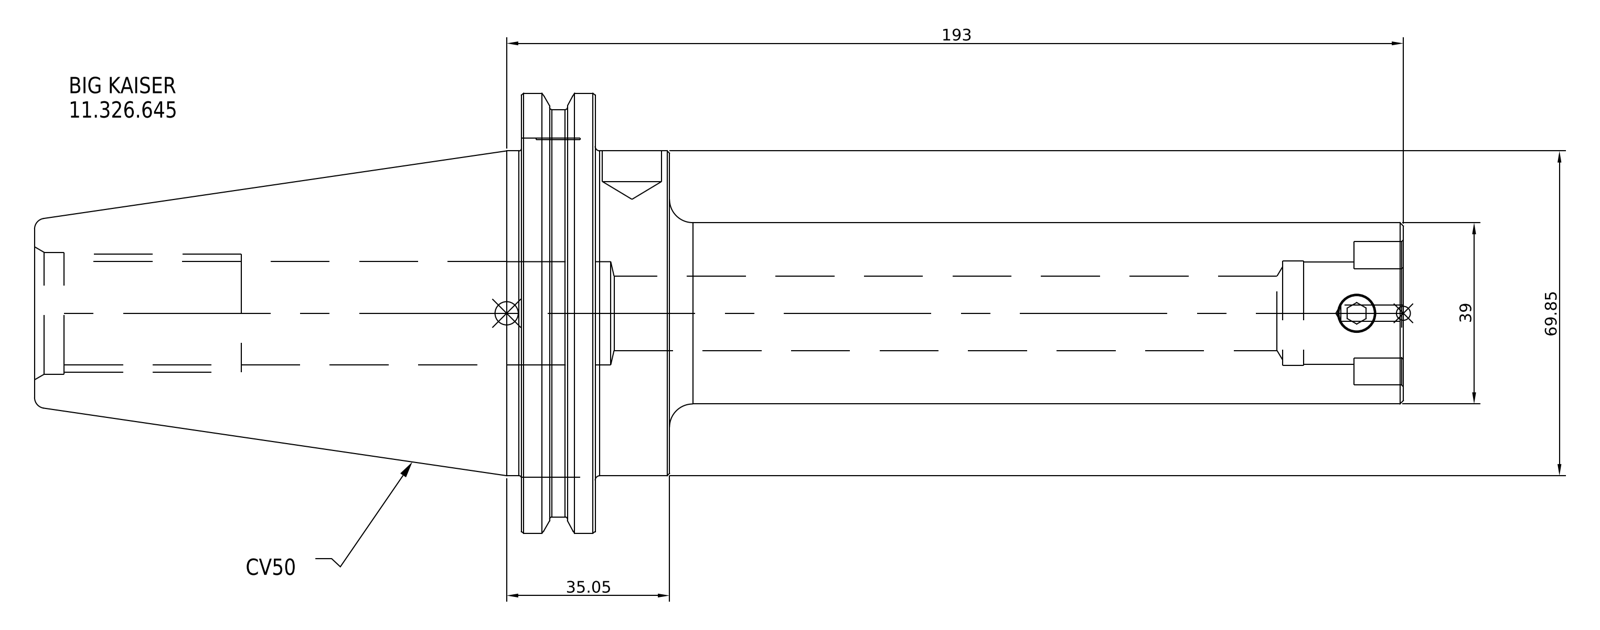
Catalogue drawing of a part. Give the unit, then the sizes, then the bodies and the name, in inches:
Units: inches
Overall size (bounding box): 11.598 × 3.875 × 3.875
Round bosses / shafts (diameter × count): ⌀3.875 ×1, ⌀3.594 ×1, ⌀2.75 ×1, ⌀1.535 ×1
Main face-to-face distances: 0.691, 0.628, 1.319, 5.378, 4.75, 4.059, 6.22, 6.848, 7.539, 11.598
Volume: 38.52 in³ · Surface area: 93.51 in²
Bodies: 1 solid, 16 faces (7 planar, 6 cylindrical, 3 other)
Part name (STEP PRODUCT): 11.326.645
STEP written by: SolidWorks 2021 (CONFIG_CONTROL_DESIGN)
